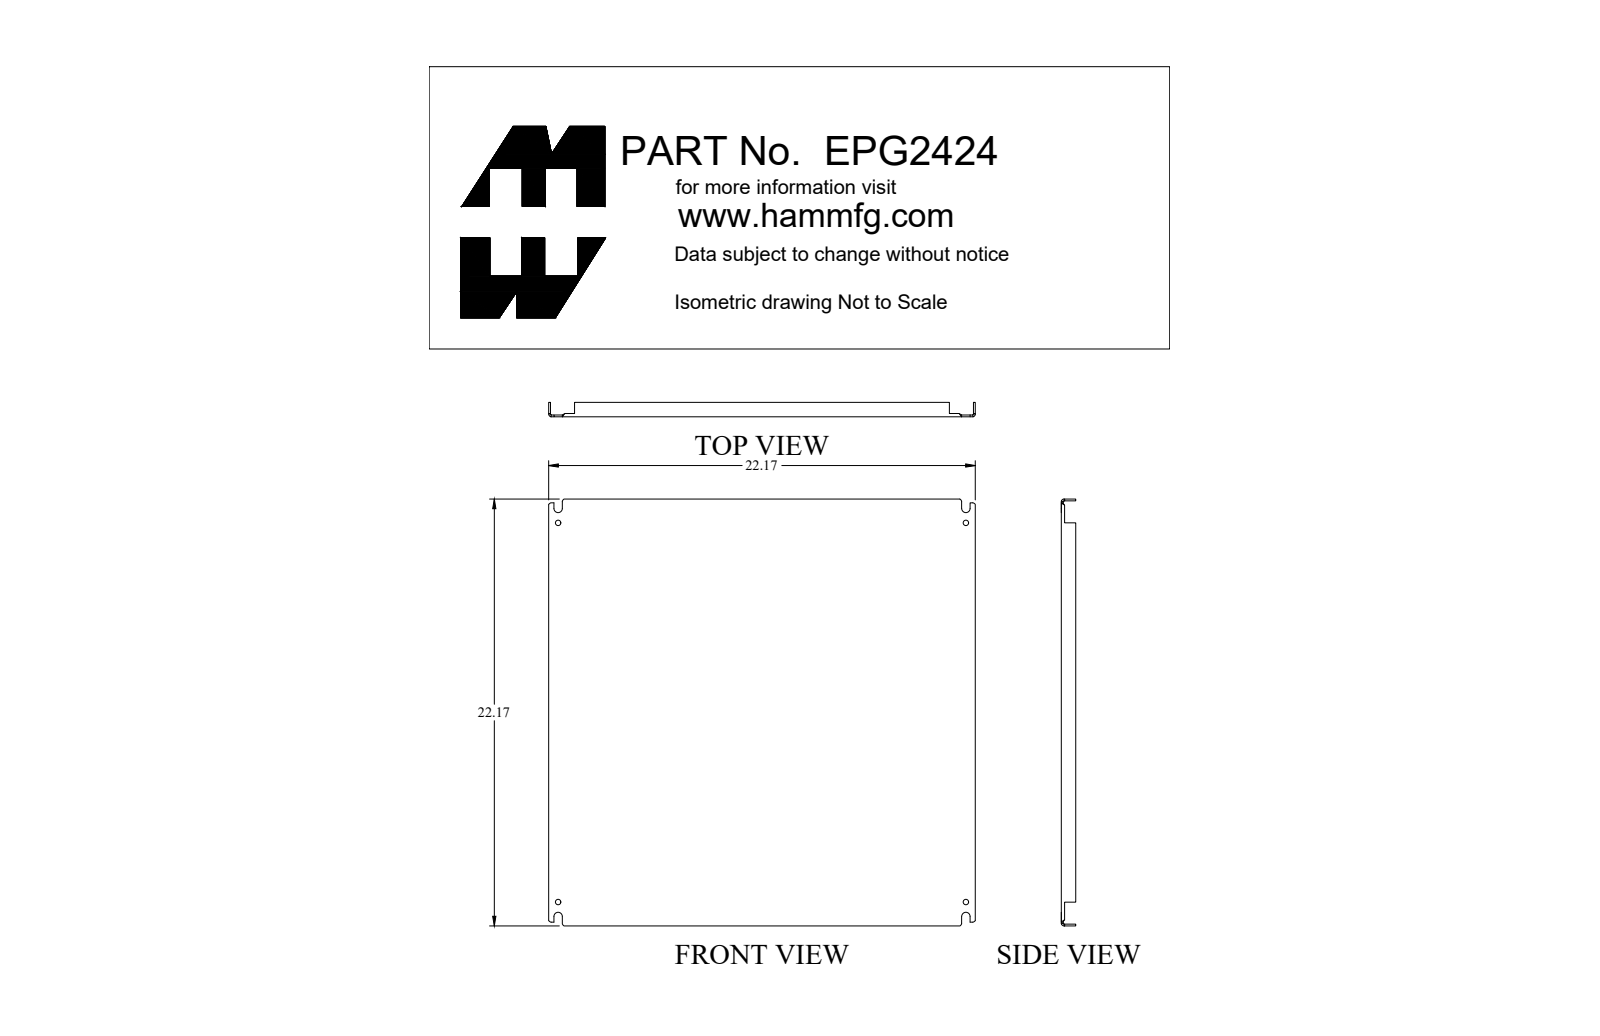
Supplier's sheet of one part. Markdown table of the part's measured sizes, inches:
| quantity | value |
| --- | --- |
| part name | EPG2424 |
| STEP written by | SolidWorks 2018 (AUTOMOTIVE_DESIGN) |
| units | inches |
| bodies | 1 solid, 128 faces (74 planar, 38 cylindrical, 16 other) |
| overall size | 22.17 × 22.17 × 0.75 |
| volume | 51.11 in³ |
| surface area | 1 086 in² |
| round holes (diameter × count) | 0.281 × 4 |
| partial cylindrical surfaces (radius × count) | 0.048 × 4, 0.063 × 4, 0.143 × 4, 0.219 × 4 |
| main face-to-face distances | 0.095, 22.075, 21.98, 22.17, 0.75, 0.655, 0.171, 0.076, 0.579, 1.235 |
| hole center spacings | 19.688, 21.188, 28.923 |
